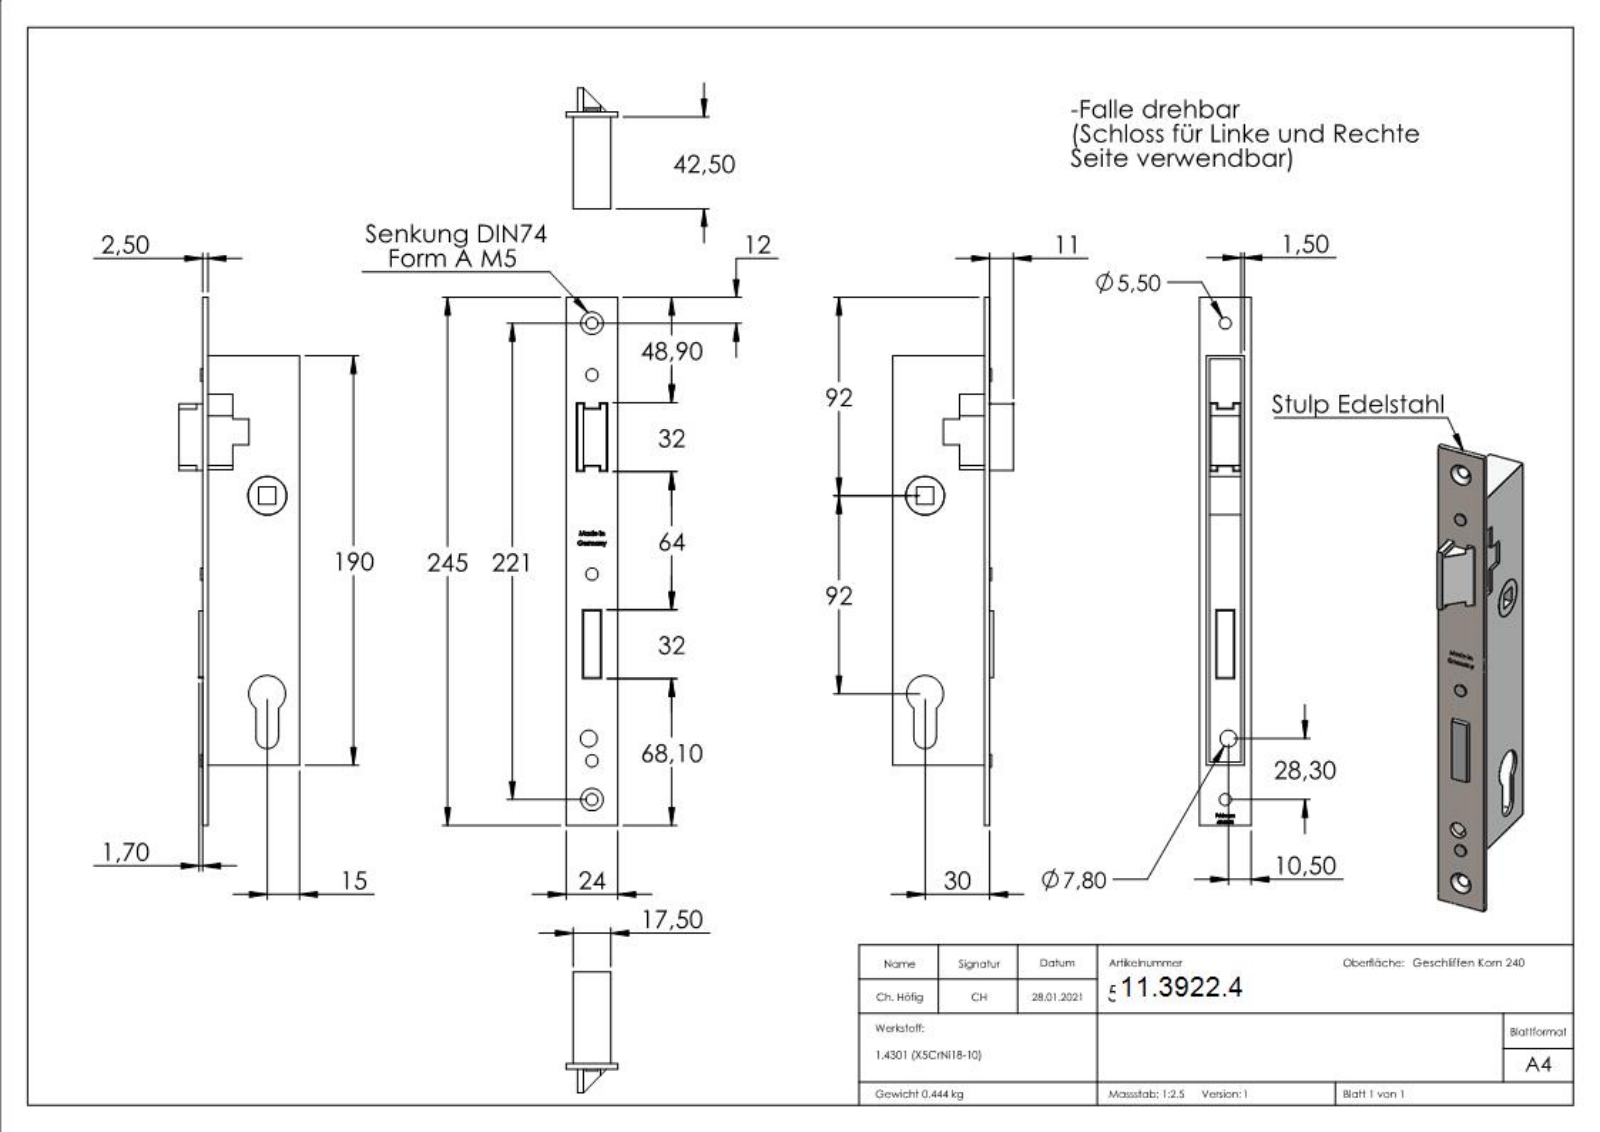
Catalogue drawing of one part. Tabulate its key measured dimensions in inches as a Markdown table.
| quantity | value |
| --- | --- |
| part name | 50106 |
| STEP written by | SolidWorks 2015 (CONFIG_CONTROL_DESIGN) |
| units | inches |
| bodies | 4 solids, 468 faces (272 planar, 24 cylindrical, 172 other) |
| overall size | 9.646 × 2.205 × 0.945 |
| volume | 3.459 in³ |
| surface area | 79.36 in² |
| round holes (diameter × count) | 0.217 × 2, 0.307 × 1, 0.709 × 1 |
| round bosses / shafts (diameter × count) | 0.224 × 3, 0.701 × 1 |
| partial cylindrical surfaces (radius × count) | 0.207 × 1, 0.335 × 1 |
| main face-to-face distances | 0.059, 0.63, 0.689, 0.571, 0.098, 0.02, 0.551, 0.079, 0.61, 0.112 |
| hole center spacings | 1.116, 7.587, 8.701 |
